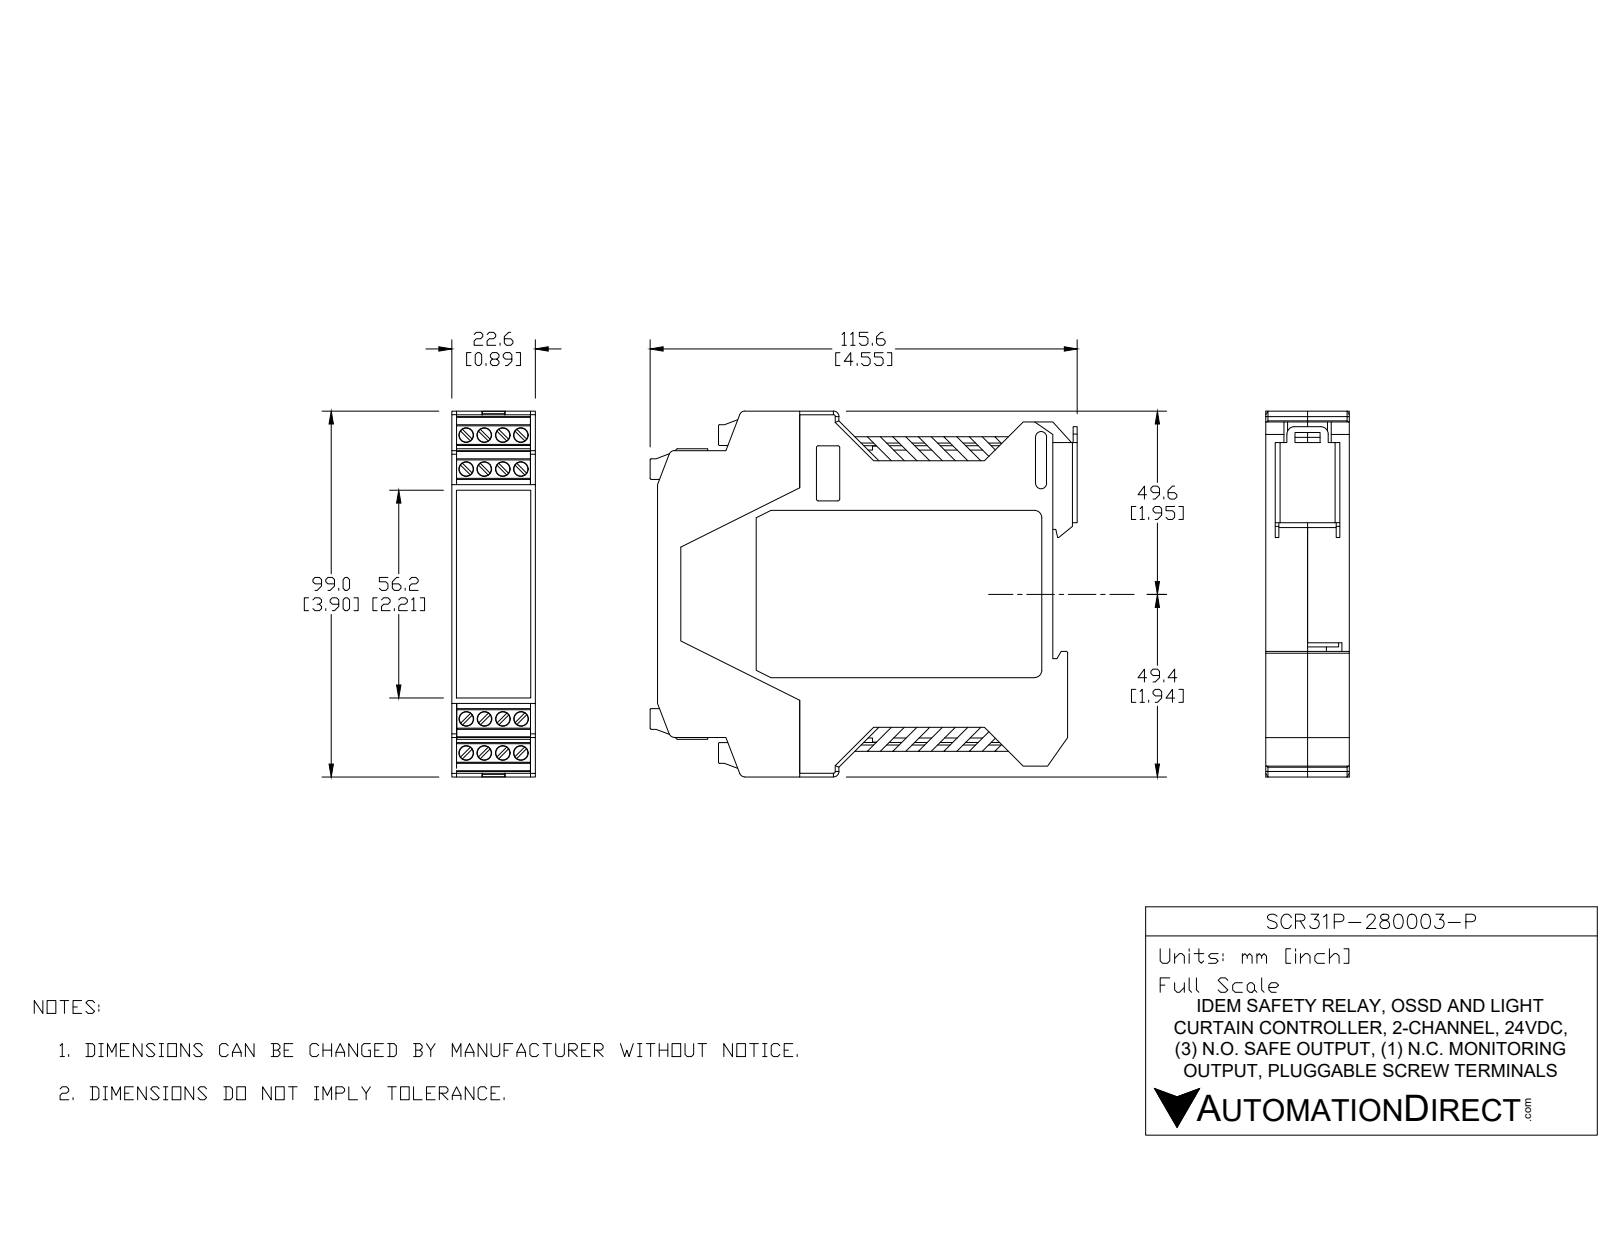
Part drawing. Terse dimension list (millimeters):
name: 280-Viper-22-P (STEP format)
written by: SolidWorks 2015 (CONFIG_CONTROL_DESIGN)
unit: mm
bodies: 14 solids, 2339 faces (1902 planar, 393 cylindrical, 44 other)
size: 115.6 × 99 × 22.6
volume: 68 441 mm³; area: 76 635 mm²
holes: 16× ⌀4, 2× ⌀2
bosses: 16× ⌀3.8, 16× ⌀1.4, 8× ⌀2.8, 2× ⌀1.9
rounds: 80× R0.2, 24× R0.3, 22× R1.2, 21× R0.5, 10× R1.5, 8× R2.92, 6× R0.25, 4× R0.8
face distances: 21.1, 1.5, 1.3, 22.4, 20.9, 19.6, 22.6, 11.3, 11.1, 9.8
hole spacings: 76.96, 4.9, 9.2, 9.9, 76.8, 77.44, 5, 10.42
